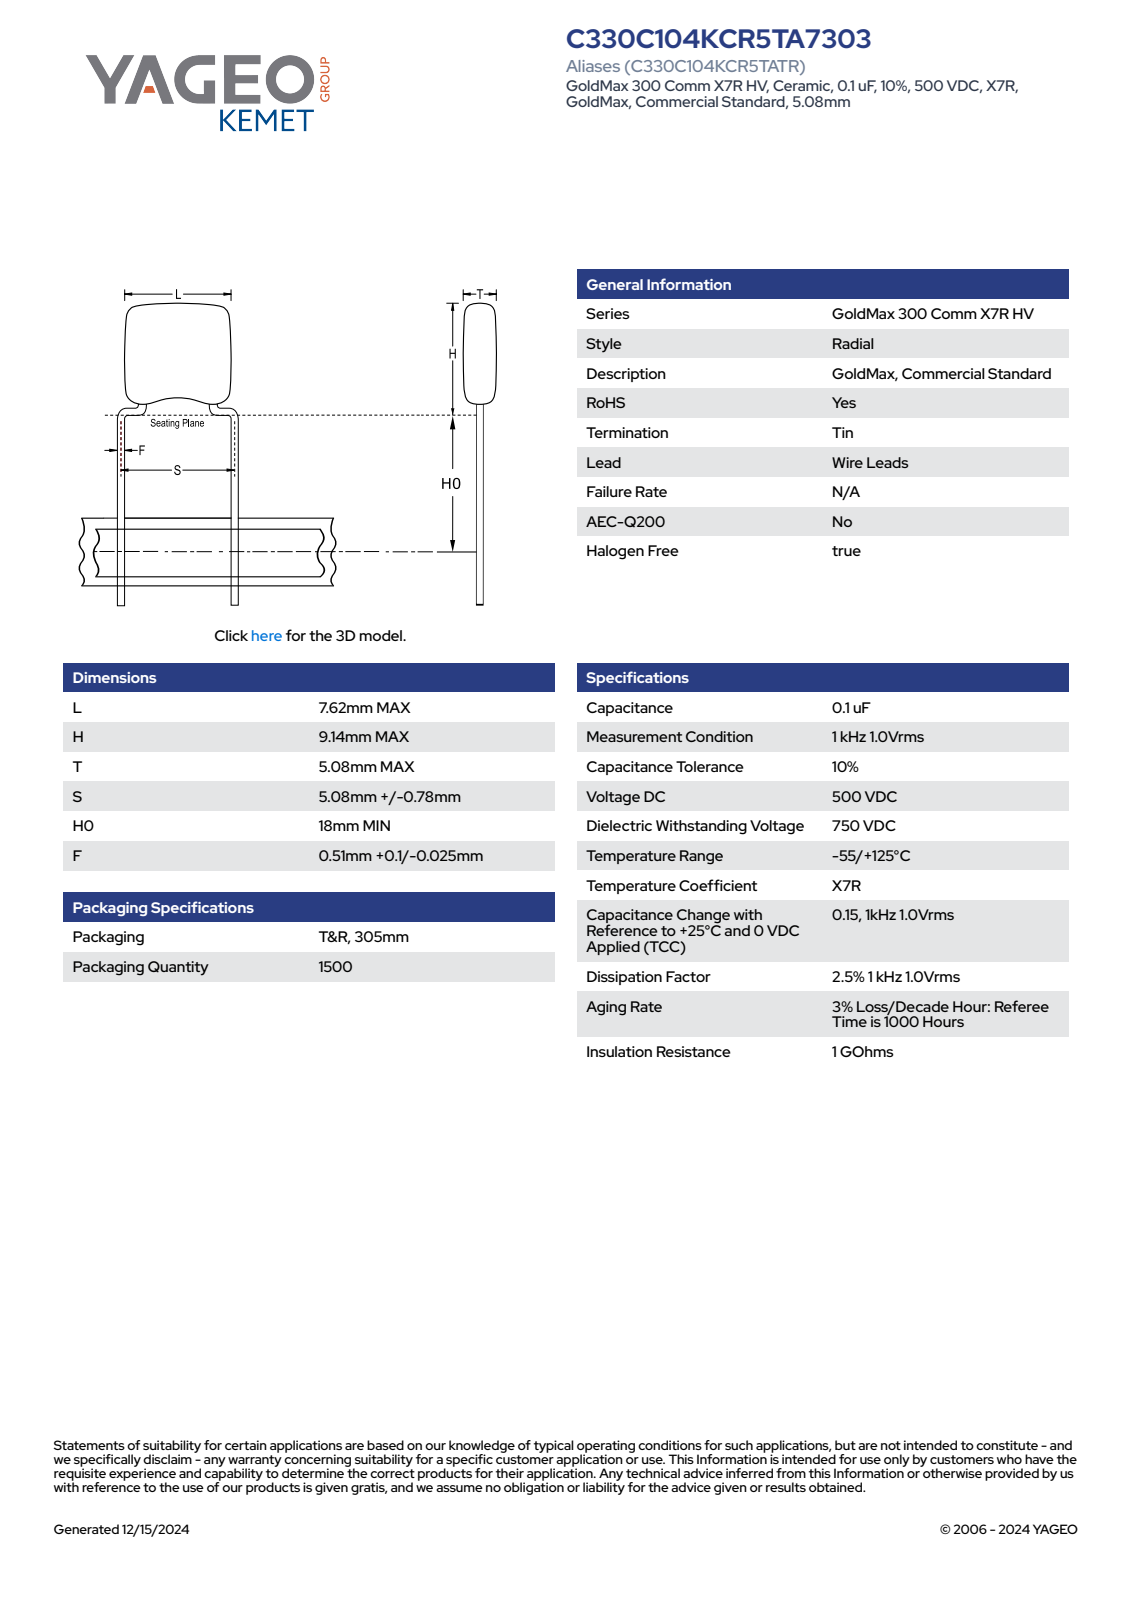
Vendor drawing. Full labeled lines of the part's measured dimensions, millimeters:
Part name (STEP PRODUCT): CCR_SB_7.62X9.14_L7.62H9.14T5.08S5.08H018F0.51
STEP written by: SolidWorks 2014 (AUTOMOTIVE_DESIGN)
Units: millimetres
Bodies: 4 solids, 97 faces (65 planar, 14 cylindrical, 18 other)
Overall size (bounding box): 27.14 × 7.62 × 5.08
Volume: 274 mm³ · Surface area: 298 mm²
Round bosses / shafts (diameter × count): ⌀0.51 ×2
Partial cylindrical surfaces — rounded edges, fillets, slot ends (radius × count): R1 ×10
Main face-to-face distances: 5.08, 7.62, 7.22, 3.9, 3.32, 3.26, 0.64, 3.96, 0.58, 0.52
